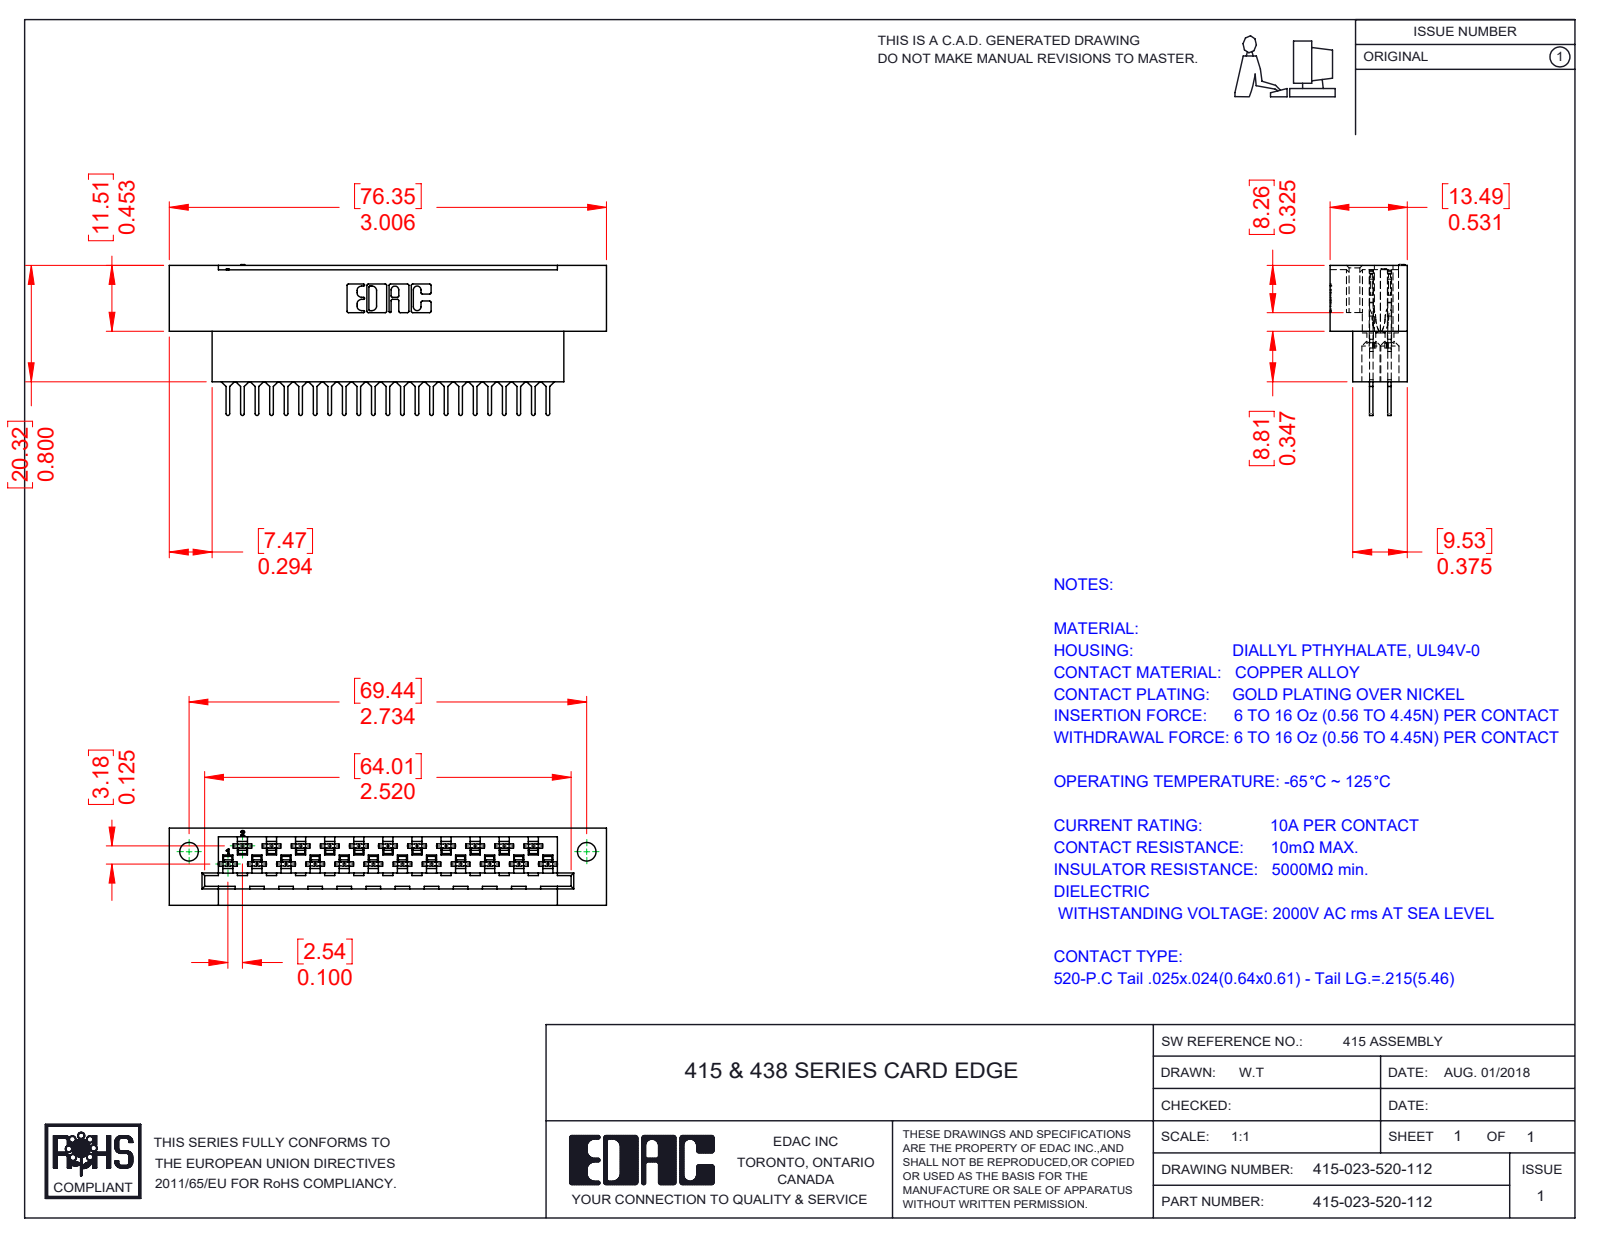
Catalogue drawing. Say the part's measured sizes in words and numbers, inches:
The part is named "415-023-520-112; 415-210-001_415-210-023-112; 516-290-001_520". Its 3-D file was written by "SolidWorks 2016 (CONFIG_CONTROL_DESIGN)". It is 24 solids with 2398 faces: 1527 planar, 642 cylindrical and 229 other. Overall it measures 3.006 by 1.036 by 0.531 inches. Its volume is 0.779 cubic inches and its surface area 23.58 square inches. Round holes: 23 of diameter 0.05, 23 of diameter 0.13, 2 of diameter 0.128. Partial cylindrical surfaces (rounded edges, fillets, slot ends): 92 of radius 0.012, 92 of radius 0.022, 46 of radius 0.007, 46 of radius 0.008, 46 of radius 0.016, 46 of radius 0.08, 23 of radius 0.013, 22 of radius 0.01. The main face-to-face distances are 0.125, 0.024, 0.074, 0.531, 0.05, 0.295, 0.8, 0.26, 0.271, 0.236. The hole center spacings are 0.2, 0.4, 0.6, 0.8, 1, 0.1, 0.16, 1.2.
